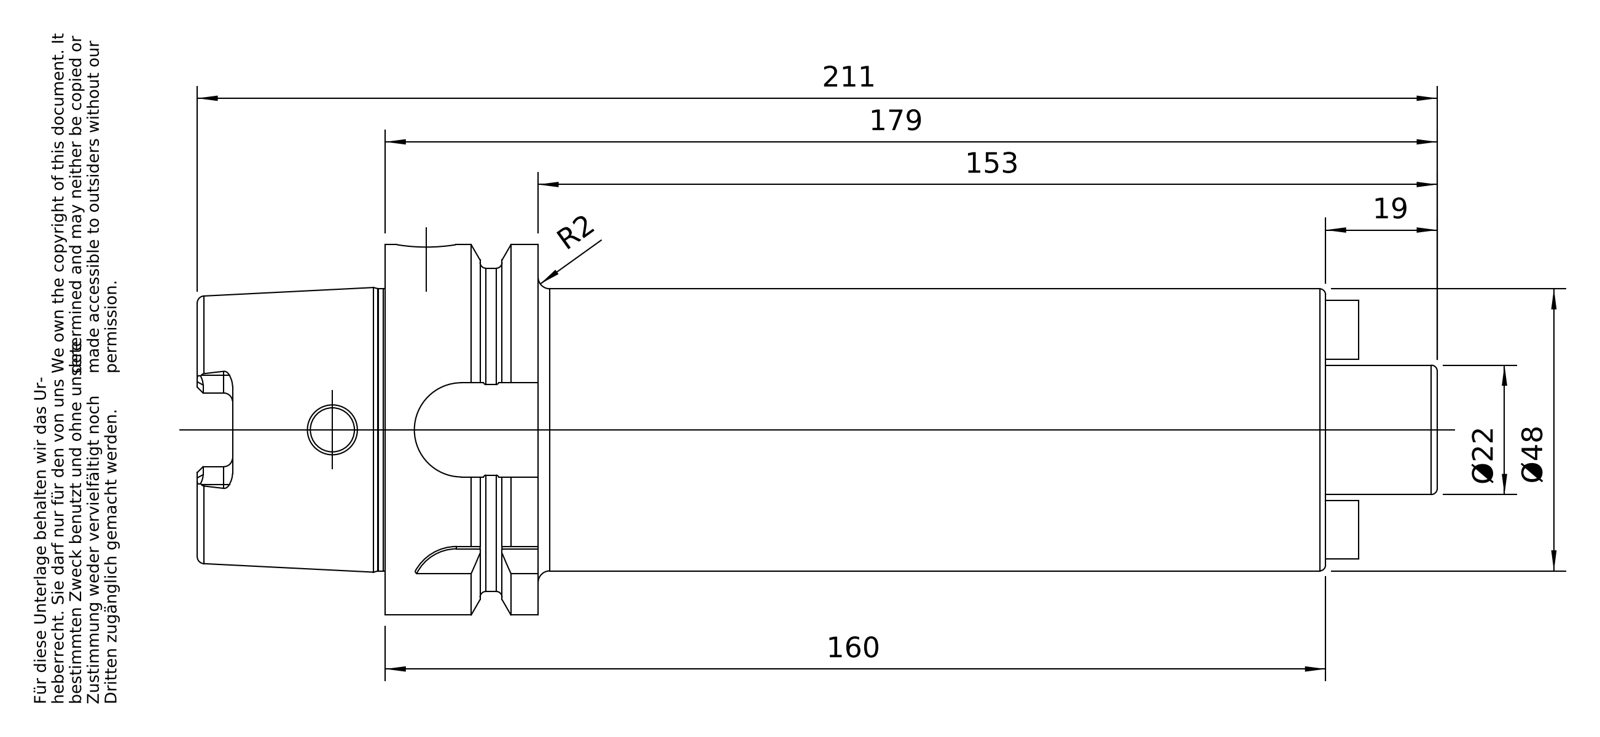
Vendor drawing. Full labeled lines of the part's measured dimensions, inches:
Part name (STEP PRODUCT): A63-052-22
STEP written by: PRO/ENGINEER BY PARAMETRIC TECHNOLOGY CORPORATION, 2010430 (CONFIG_CONTROL_DESIGN)
Units: inches
Bodies: 1 solid, 190 faces (68 planar, 52 cylindrical, 70 other)
Overall size (bounding box): 8.307 × 2.48 × 2.48
Volume: 20.19 in³ · Surface area: 71.05 in²
Round holes (diameter × count): ⌀0.394 ×2, ⌀0.295 ×1, ⌀0.335 ×1, ⌀0.666 ×1, ⌀0.721 ×1, ⌀0.735 ×1, ⌀1.339 ×1, ⌀1.575 ×1
Round bosses / shafts (diameter × count): ⌀2.48 ×1, ⌀2.165 ×1, ⌀1.891 ×1, ⌀1.89 ×1, ⌀0.866 ×1, ⌀0.709 ×1
Partial cylindrical surfaces — rounded edges, fillets, slot ends (radius × count): R0.059 ×6, R0.118 ×4, R0.315 ×1, R0.316 ×1, R0.355 ×1
Main face-to-face distances: 6.299, 1.024, 5.276, 0.394, 0.63, 5.906, 1.26, 1.654, 2.283, 7.559
